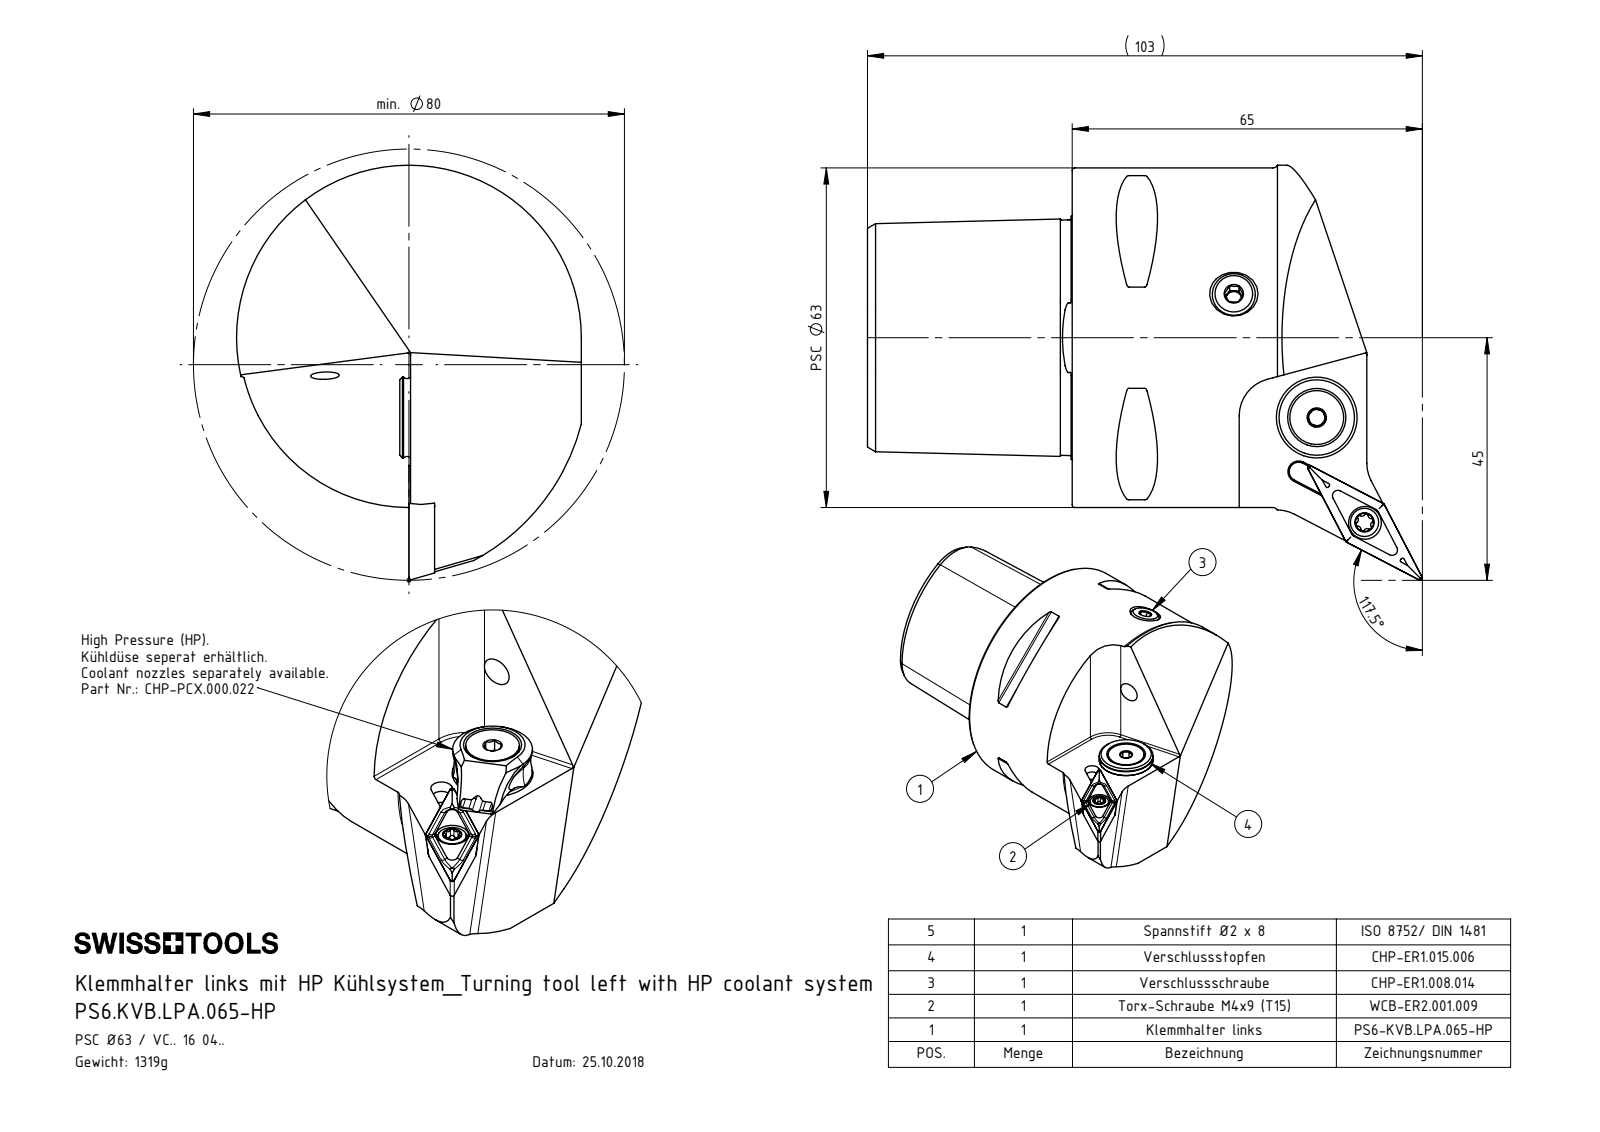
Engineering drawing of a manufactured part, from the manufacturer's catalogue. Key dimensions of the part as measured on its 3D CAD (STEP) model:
Part name (STEP PRODUCT): CHP-ER1.008.014_A; DIN 3771 - 6.5x1.5; CHP-PCX.000.022_B; CHP-PCX.000.022_Dse (+7 more)
STEP written by: SolidWorks 2017 (CONFIG_CONTROL_DESIGN)
Units: millimetres
Bodies: 9 solids, 486 faces (105 planar, 133 cylindrical, 248 other)
Overall size (bounding box): 103 × 76.57 × 64
Volume: 163 652 mm³ · Surface area: 31 793 mm²
Round holes (diameter × count): ⌀4.2 ×2, ⌀5 ×2, ⌀1.2 ×1, ⌀2 ×1, ⌀3 ×1, ⌀3.3 ×1, ⌀4 ×1, ⌀4.4 ×1, ⌀5.3 ×1, ⌀6.1 ×1, ⌀7 ×1, ⌀8.1 ×1
Round bosses / shafts (diameter × count): ⌀63 ×1, ⌀14.85 ×1, ⌀13.4 ×1, ⌀10 ×1, ⌀8 ×1, ⌀5.5 ×1, ⌀5.25 ×1, ⌀5 ×1
Partial cylindrical surfaces — rounded edges, fillets, slot ends (radius × count): R0.5 ×12, R1 ×7, R0.34 ×6, R0.59 ×6, R6 ×3, R7 ×3, R1.1 ×2, R1.2 ×2
Main face-to-face distances: 31, 38, 69, 24.88, 11, 27, 42, 4.46, 27.24, 31.7
Hole centre spacings: 4.5, 18.63, 18.73, 21.38, 21.48, 27.5, 36.53, 41.01
